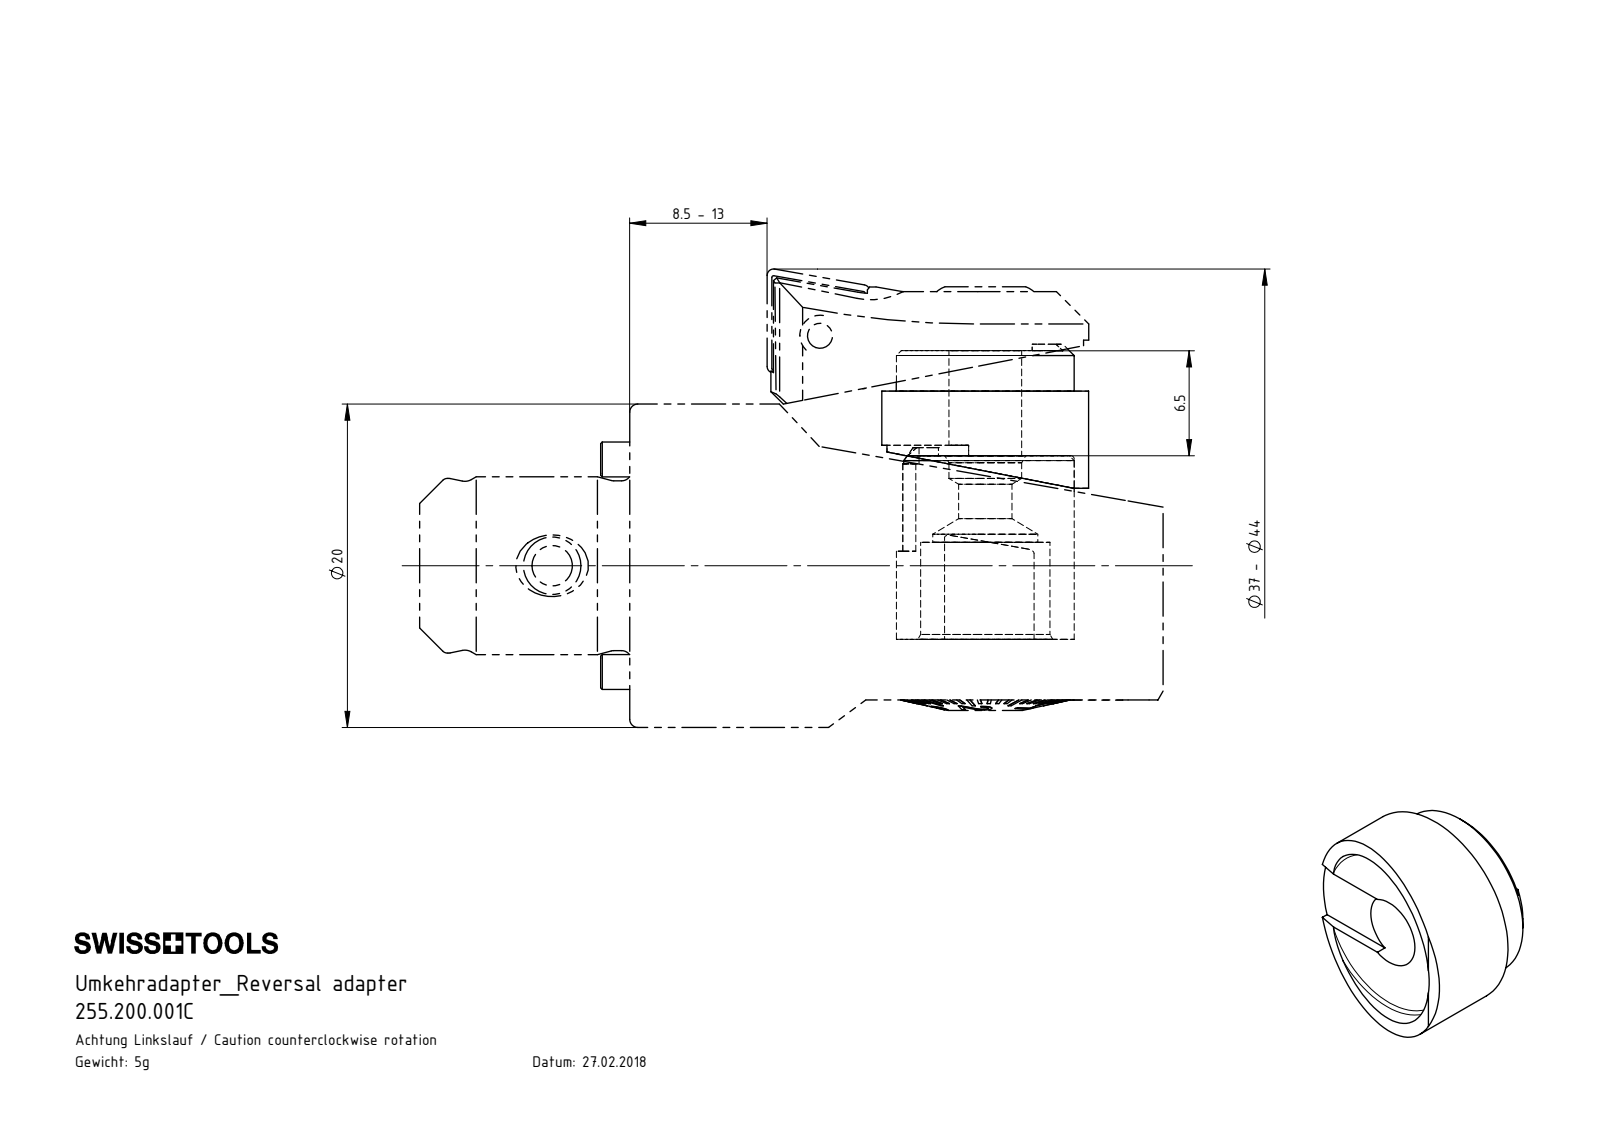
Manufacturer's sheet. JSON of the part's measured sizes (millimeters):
{"part_name": "F20-U00.001.006_B; 255.200.001C", "step_written_by": "SolidWorks 2017 (CONFIG_CONTROL_DESIGN)", "units": "millimeters", "bodies": {"solids": 1, "faces": 29, "planar": 13, "cylindrical": 11, "other": 5}, "overall_size": [12.8, 12.8, 8.9], "volume_mm3": 671, "surface_area_mm2": 632, "round_holes": [[4.5, 1], [11, 1]], "round_bosses_or_shafts": [[12.8, 1]], "partial_cylinders_radius": [[0.3, 2]], "face_to_face_distances": [6.5, 4, 2.5, 5.85, 3.35, 0.65, 0.4, 2.9, 6.25, 6.9]}
